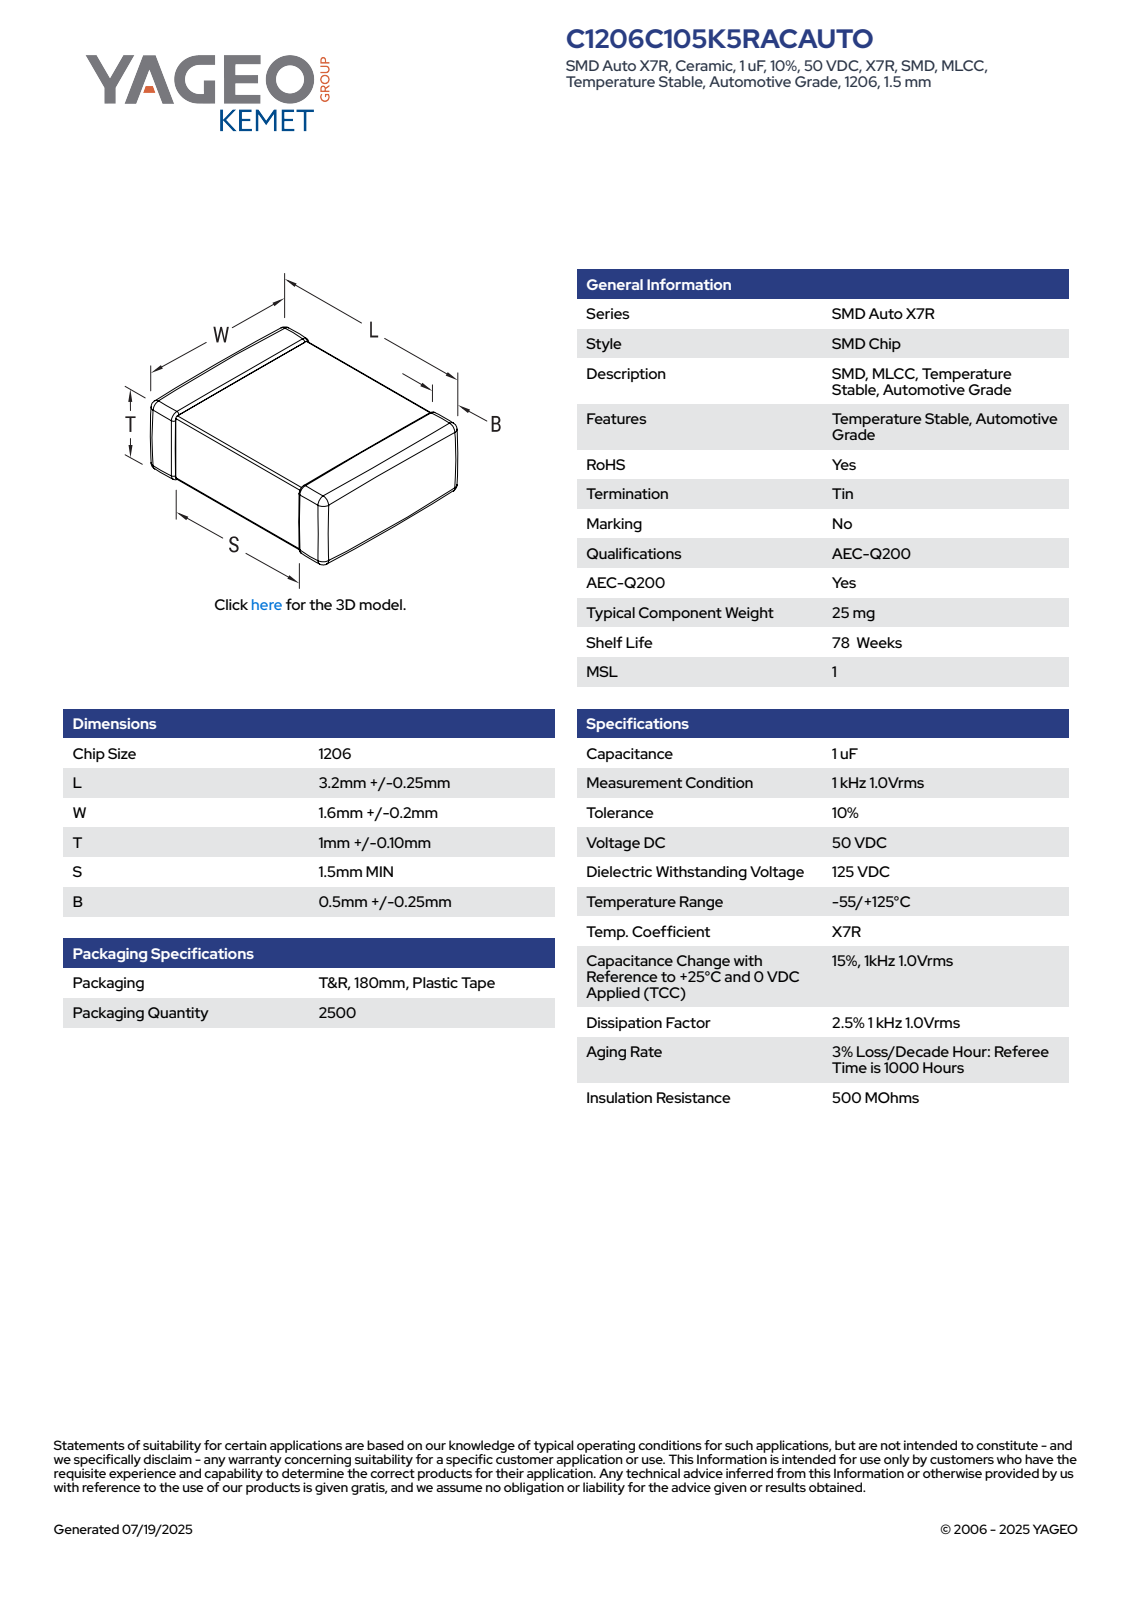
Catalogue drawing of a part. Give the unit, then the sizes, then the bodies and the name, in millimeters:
Units: millimetres
Overall size (bounding box): 3.45 × 1.8 × 1.1
Main face-to-face distances: 1.06, 1.02, 1.76, 1.1, 1.72, 3.45, 1.8, 1.07, 1.03, 1.6
Volume: 6 mm³ · Surface area: 24 mm²
Bodies: 4 solids, 125 faces (71 planar, 38 cylindrical, 16 other)
Part name (STEP PRODUCT): CCS_CCSTD_1206_L3.45W1.8T1.1B0.5
STEP written by: SolidWorks 2021 (AUTOMOTIVE_DESIGN)
